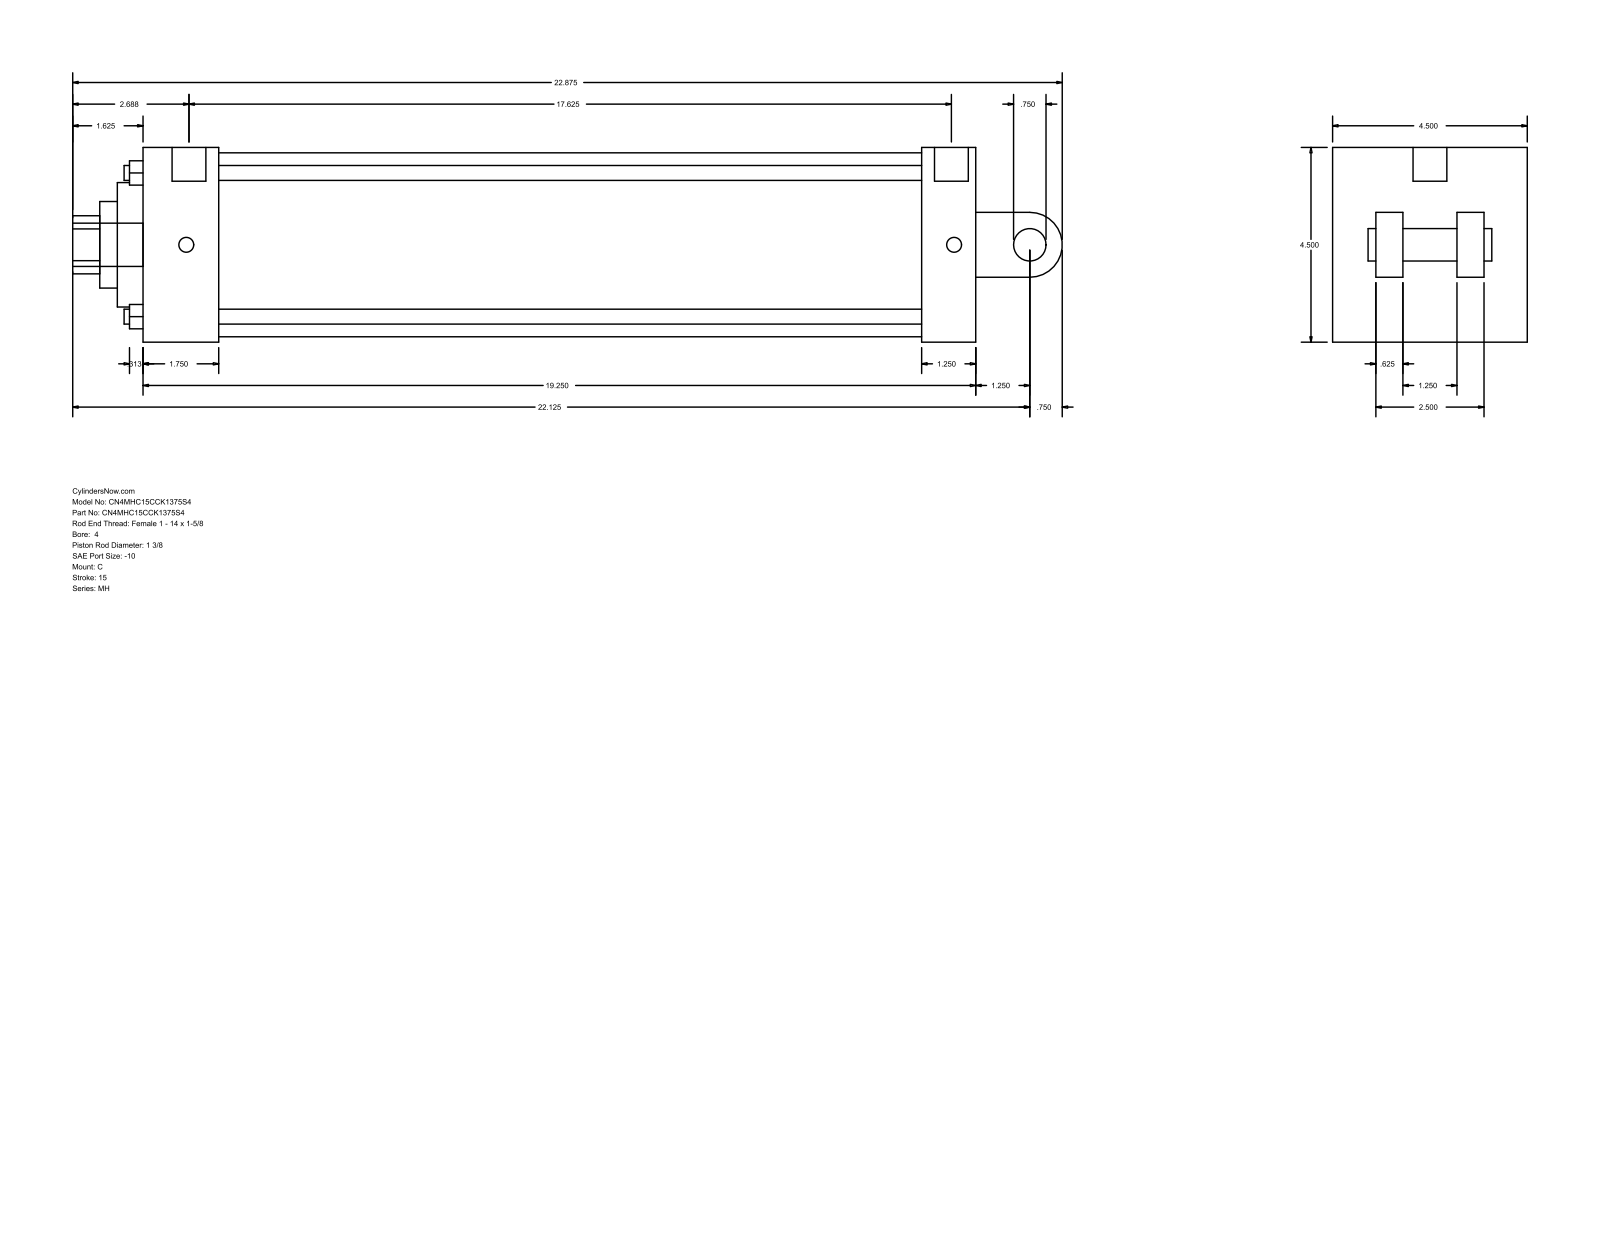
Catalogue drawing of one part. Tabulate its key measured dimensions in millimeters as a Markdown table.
| quantity | value |
| --- | --- |
| part name | MH_C__0400_1.375 |
| STEP written by | GSSL Pune (CONFIG_CONTROL_DESIGN) |
| units | millimeters |
| bodies | 0 solids, 101 faces (71 planar, 30 cylindrical, 0 other) |
| overall size | 581.02 × 114.3 × 114.3 |
| round holes (diameter × count) | 8.76 × 4, 8.73 × 2, 19.84 × 1, 34.92 × 1, 50.8 × 1, 73.03 × 1, 107.95 × 1 |
| round bosses / shafts (diameter × count) | 8.73 × 2, 25.4 × 1, 19.84 × 1, 19.05 × 1 |
| partial cylindrical surfaces (radius × count) | 17.06 × 1, 19.05 × 1 |
| main face-to-face distances | 114.3, 488.96, 44.45, 457.21, 412.76, 444.51, 31.75, 73.03, 41.27, 38.1 |
| hole center spacings | 59.62, 84.32, 119.25, 1.58 |
